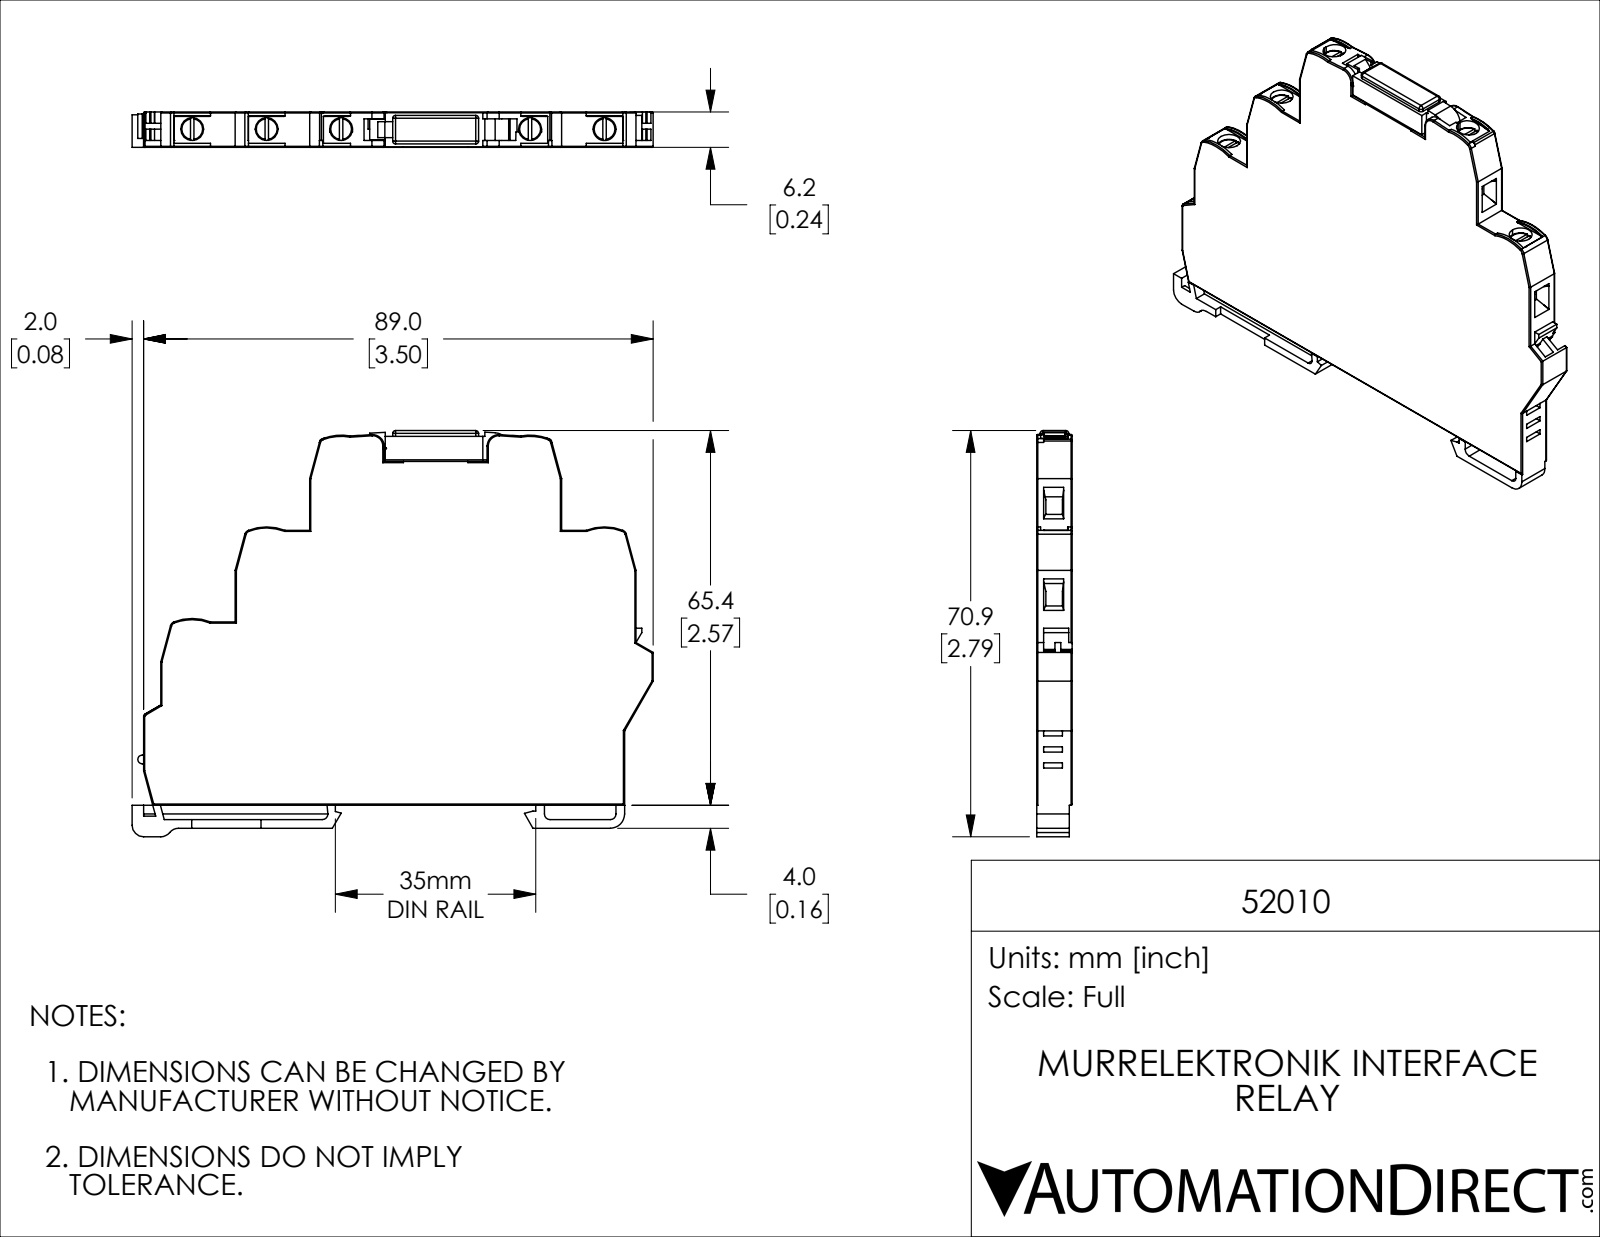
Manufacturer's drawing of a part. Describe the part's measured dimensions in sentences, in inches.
The part is named "52010". Its 3-D file was written by "SolidWorks 2019 (CONFIG_CONTROL_DESIGN)". It is 2 solids with 566 faces: 351 planar, 147 cylindrical and 68 other. Overall it measures 3.583 by 2.791 by 0.244 inches. Its volume is 1.706 cubic inches and its surface area 20.13 square inches. Round holes: 5 of diameter 0.157, 1 of diameter 0.075. Round bosses or shafts: 1 of diameter 0.079. Partial cylindrical surfaces (rounded edges, fillets, slot ends): 56 of radius 0.008, 11 of radius 0.02, 8 of radius 0.039, 6 of radius 0.079, 5 of radius 0.03, 5 of radius 0.346, 4 of radius 0.005, 3 of radius 0.016. The main face-to-face distances are 0.244, 0.059, 0.197, 0.098, 0.157, 0.118, 0.047, 0.02, 0.039, 2.362. The hole center spacings are 0.512, 1.811, 2.323, 1.024, 1.299, 2.835.
